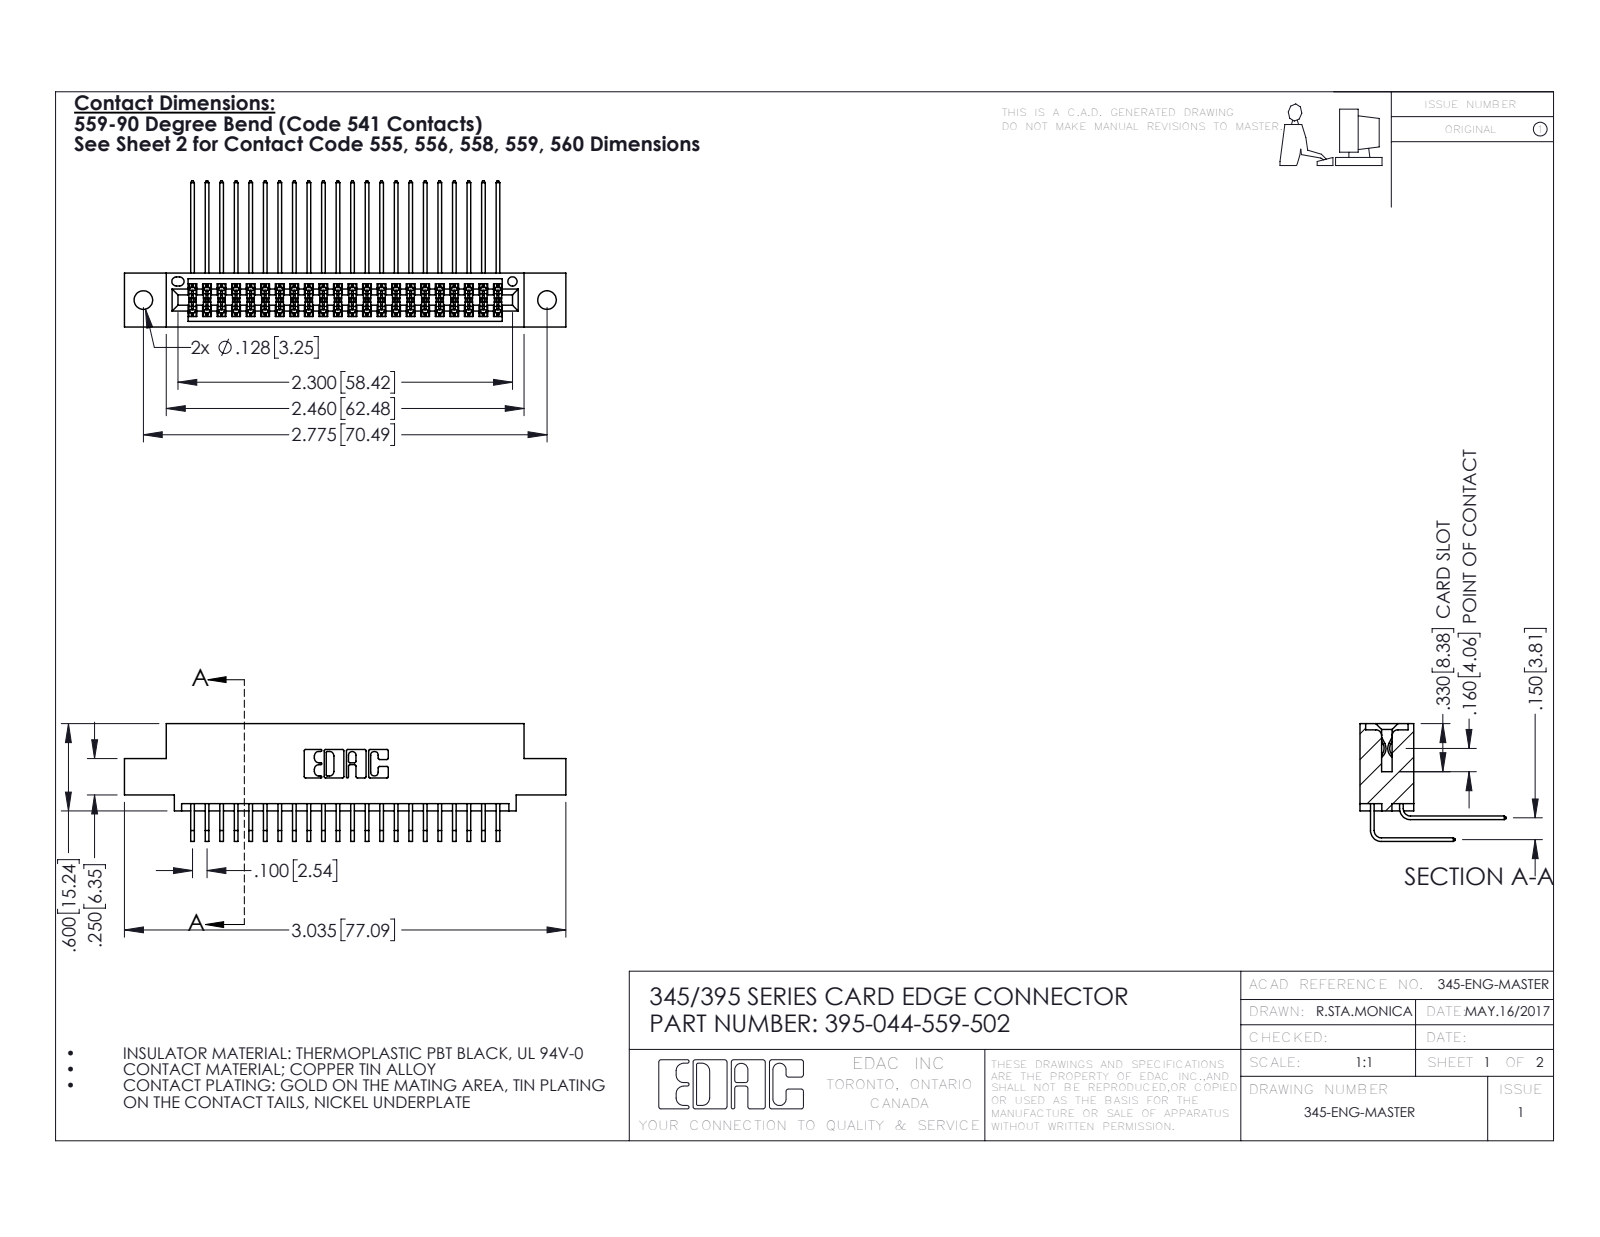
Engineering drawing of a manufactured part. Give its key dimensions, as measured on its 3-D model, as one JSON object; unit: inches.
{"part_name": "345 Part_0.110 Offset - 0.128 Dia; 345-292-001_558 559 Tail - 1; 345-292-001_559 Tail - 2; 395-044-559-502", "step_written_by": "SolidWorks 2016 (CONFIG_CONTROL_DESIGN)", "units": "inches", "bodies": {"solids": 45, "faces": 2418, "planar": 1624, "cylindrical": 794, "other": 0}, "overall_size": [3.035, 1.005, 0.809], "volume_in3": 0.454, "surface_area_in2": 18.03, "round_holes": [[0.128, 2], [0.064, 1]], "partial_cylinders_radius": [[0.006, 67], [0.01, 22], [0.007, 6], [0.031, 6], [0.026, 3], [0.014, 2], [0.019, 2], [0.022, 2]], "face_to_face_distances": [0.072, 0.298, 0.2, 0.37, 0.098, 0.272, 0.025, 0.225, 0.15, 0.175], "hole_center_spacings": [0.27, 2.541, 2.775]}
